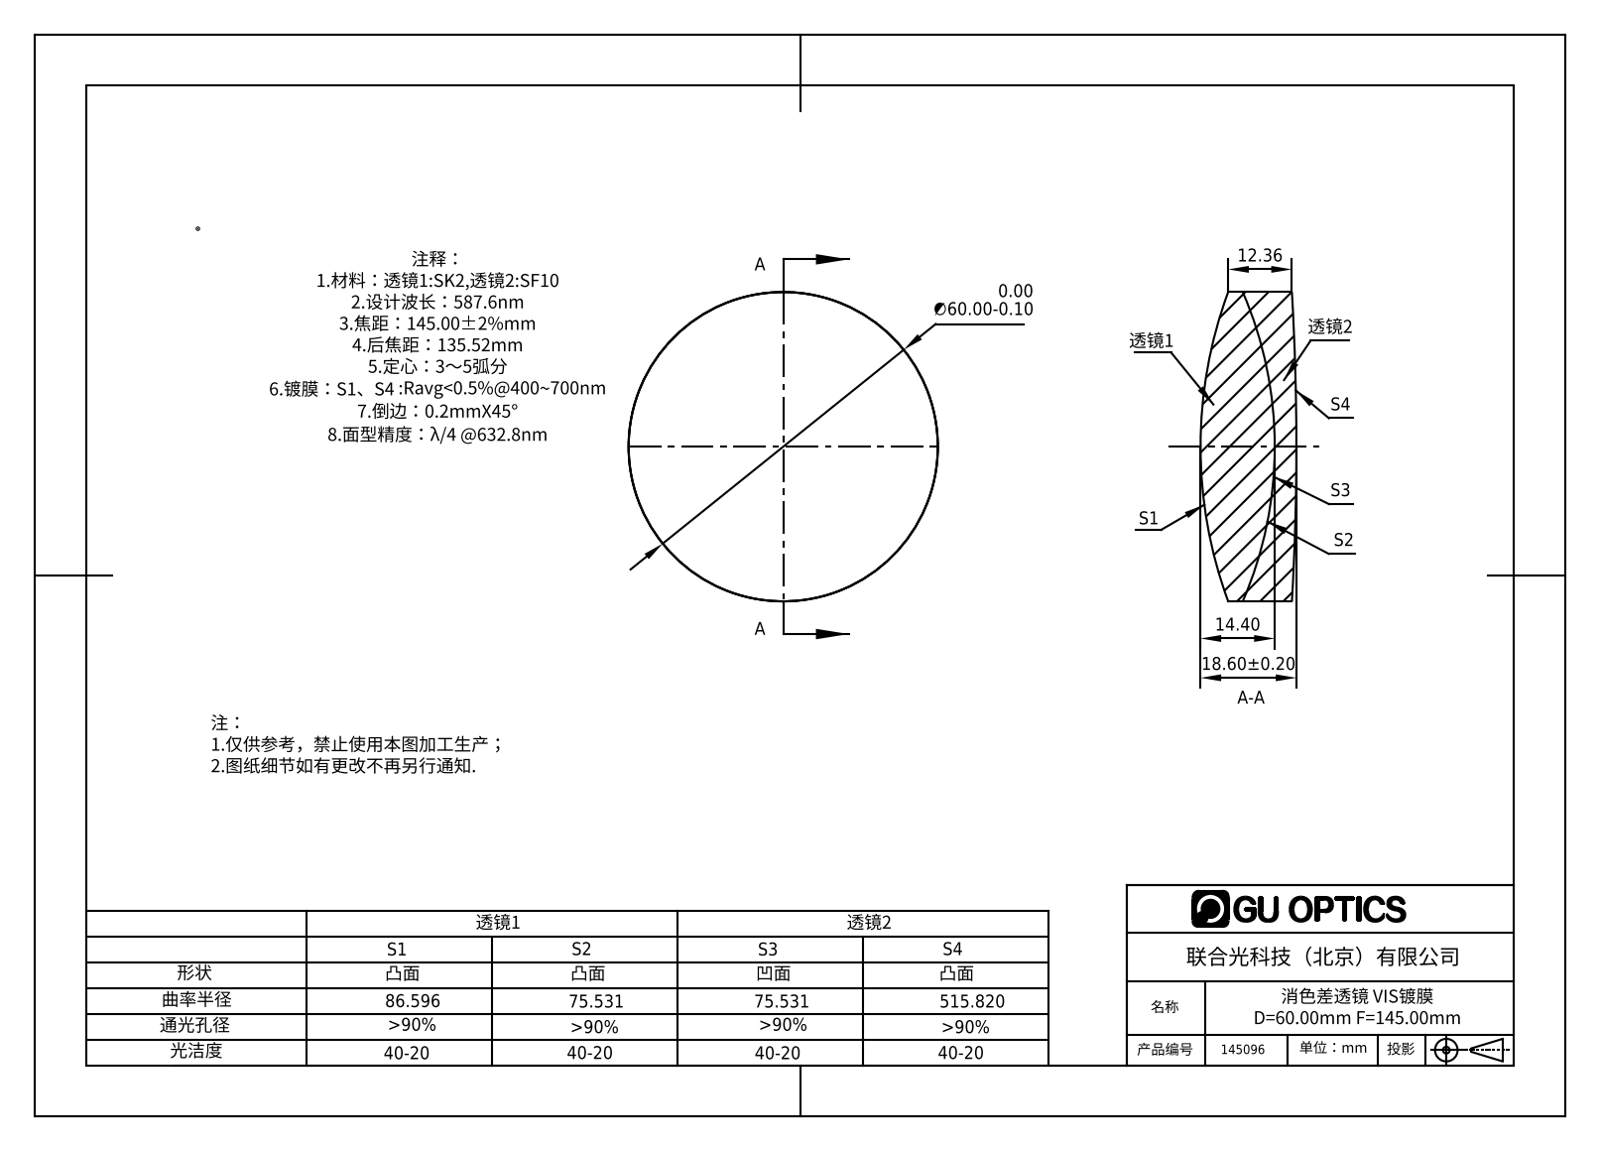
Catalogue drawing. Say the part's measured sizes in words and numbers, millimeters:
The part is named "145096". Its 3-D file was written by "SolidWorks 2016 (AUTOMOTIVE_DESIGN)". It is 2 solids with 12 faces: 0 planar, 4 cylindrical and 8 other. Overall it measures 60 by 60 by 18.6 millimeters. Its volume is 43 856 cubic millimeters and its surface area 13 976 square millimeters. Round bosses or shafts: 1 of diameter 60.
